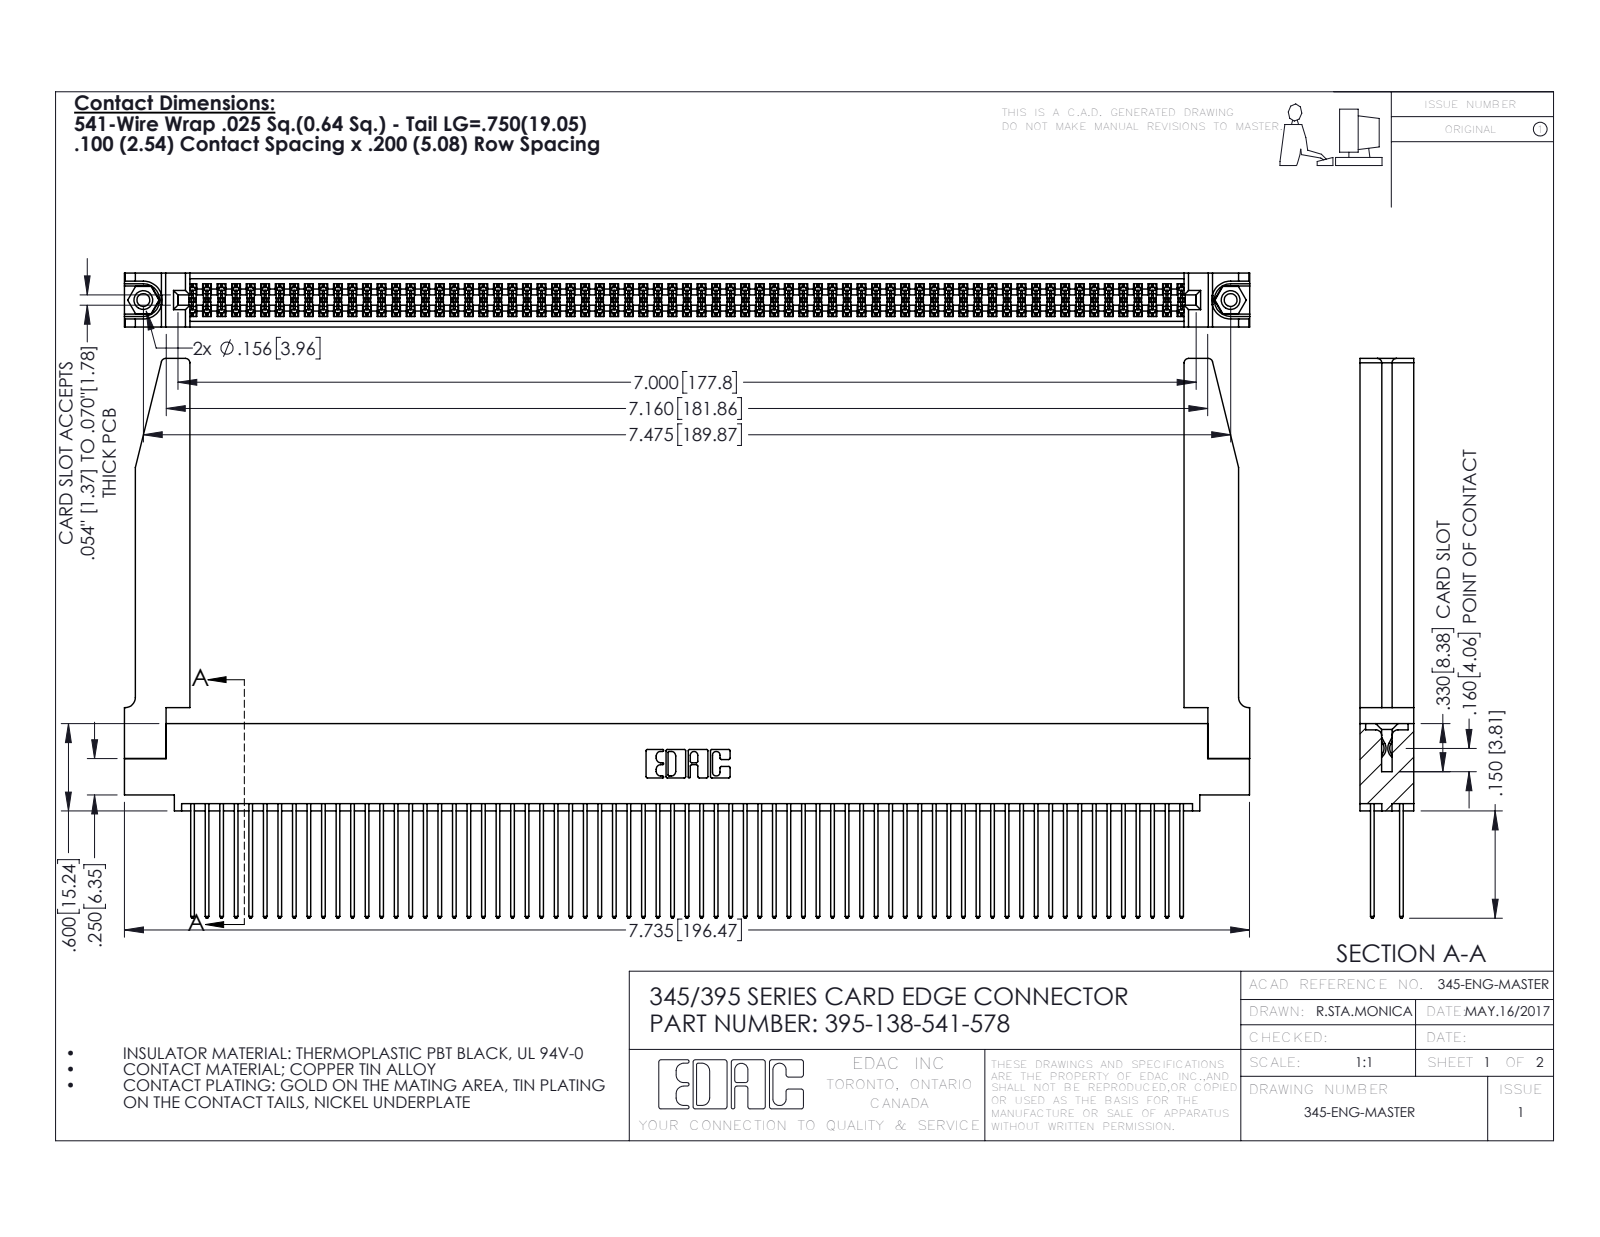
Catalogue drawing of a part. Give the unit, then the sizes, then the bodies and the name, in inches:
Units: inches
Overall size (bounding box): 7.736 × 3.847 × 0.37
Round holes (diameter × count): ⌀0.089 ×2, ⌀0.125 ×2, ⌀0.156 ×2, ⌀0.064 ×1
Round bosses / shafts (diameter × count): ⌀0.155 ×2
Partial cylindrical surfaces — rounded edges, fillets, slot ends (radius × count): R0.006 ×207, R0.01 ×138, R0.01 ×22, R0.03 ×8, R0.007 ×6, R0.031 ×6, R0.026 ×3, R0.014 ×2
Main face-to-face distances: 0.072, 0.298, 0.098, 0.272, 0.025, 0.2, 0.37, 0.225, 0.175, 0.149
Hole centre spacings: 0.27, 7.239, 7.475
Volume: 1.698 in³ · Surface area: 63.28 in²
Bodies: 143 solids, 7264 faces (4780 planar, 2432 cylindrical, 52 other)
Part name (STEP PRODUCT): 345-292-001_345-293-141; 345-250-001_345-250-001-102; 395-138-541-578; 345-220-078_345-220-078 (+1 more)
STEP written by: SolidWorks 2016 (CONFIG_CONTROL_DESIGN)
